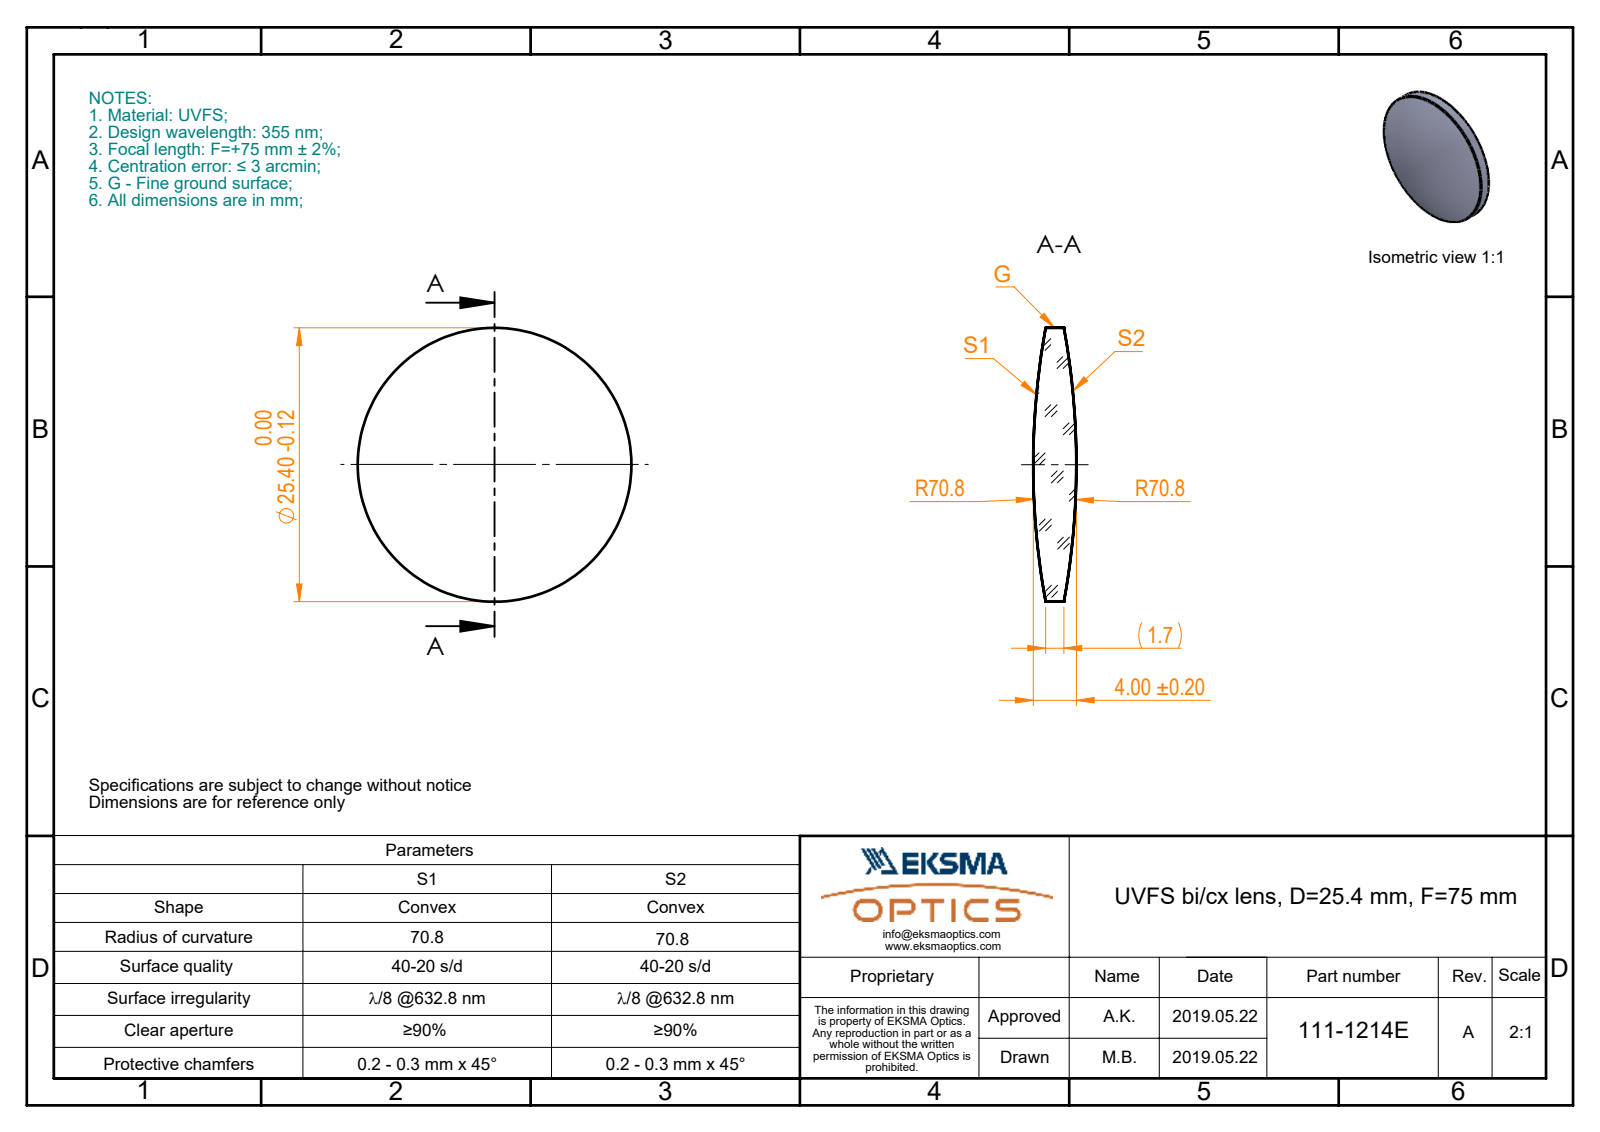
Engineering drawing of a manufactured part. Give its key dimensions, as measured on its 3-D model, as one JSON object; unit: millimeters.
{"part_name": "111-1214E UVFS bi-cx 25.4 F75", "step_written_by": "SolidWorks 2017 (CONFIG_CONTROL_DESIGN)", "units": "millimeters", "bodies": {"solids": 1, "faces": 6, "planar": 0, "cylindrical": 2, "other": 4}, "overall_size": [25.4, 25.4, 4], "volume_mm3": 1446, "surface_area_mm2": 1158, "round_bosses_or_shafts": [[25.4, 1]]}
